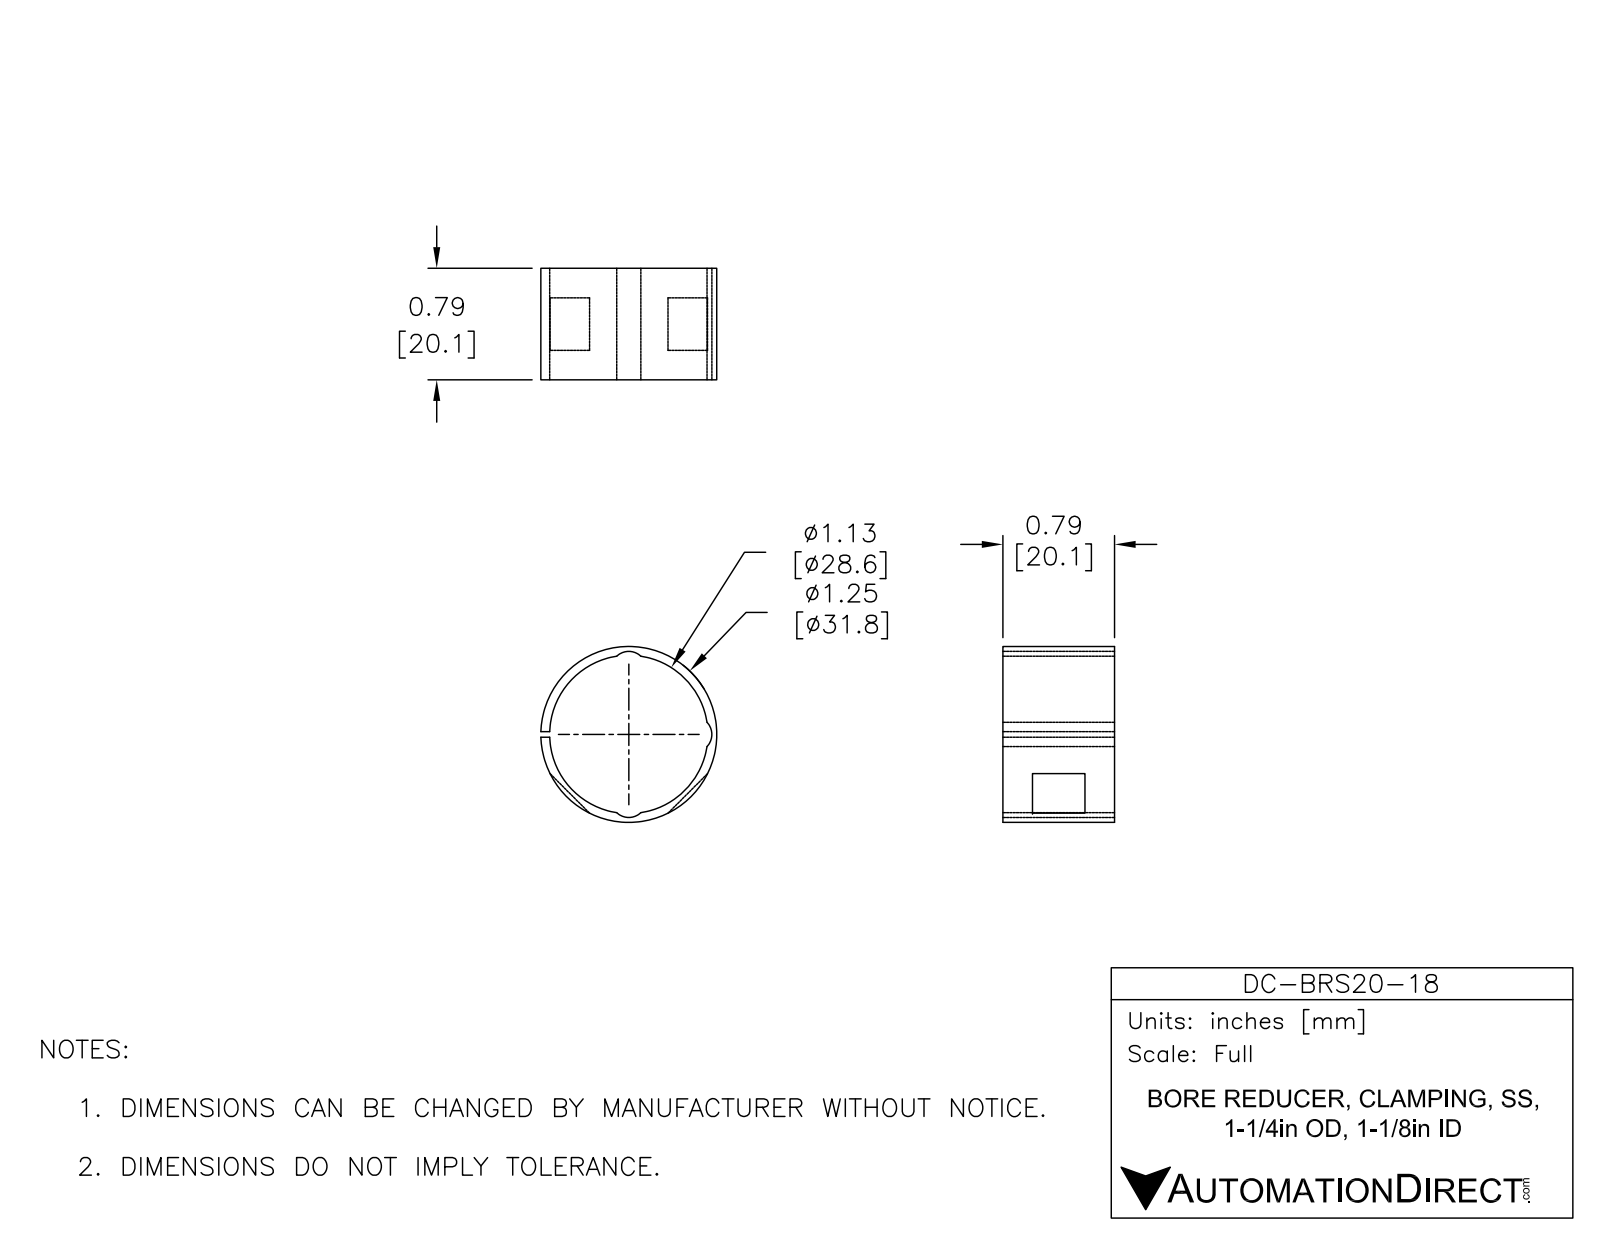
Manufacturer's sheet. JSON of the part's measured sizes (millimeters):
{"part_name": "DC-BR520-18", "step_written_by": "SolidWorks 2015 (AUTOMOTIVE_DESIGN)", "units": "millimeters", "bodies": {"solids": 1, "faces": 21, "planar": 10, "cylindrical": 11, "other": 0}, "overall_size": [31.75, 31.74, 20.14], "volume_mm3": 2765, "surface_area_mm2": 4170, "round_holes": [[28.58, 1]], "round_bosses_or_shafts": [[31.75, 1]], "partial_cylinders_radius": [[3.17, 3]], "face_to_face_distances": [20.14, 1.02, 5.33, 14.81, 9.48]}
